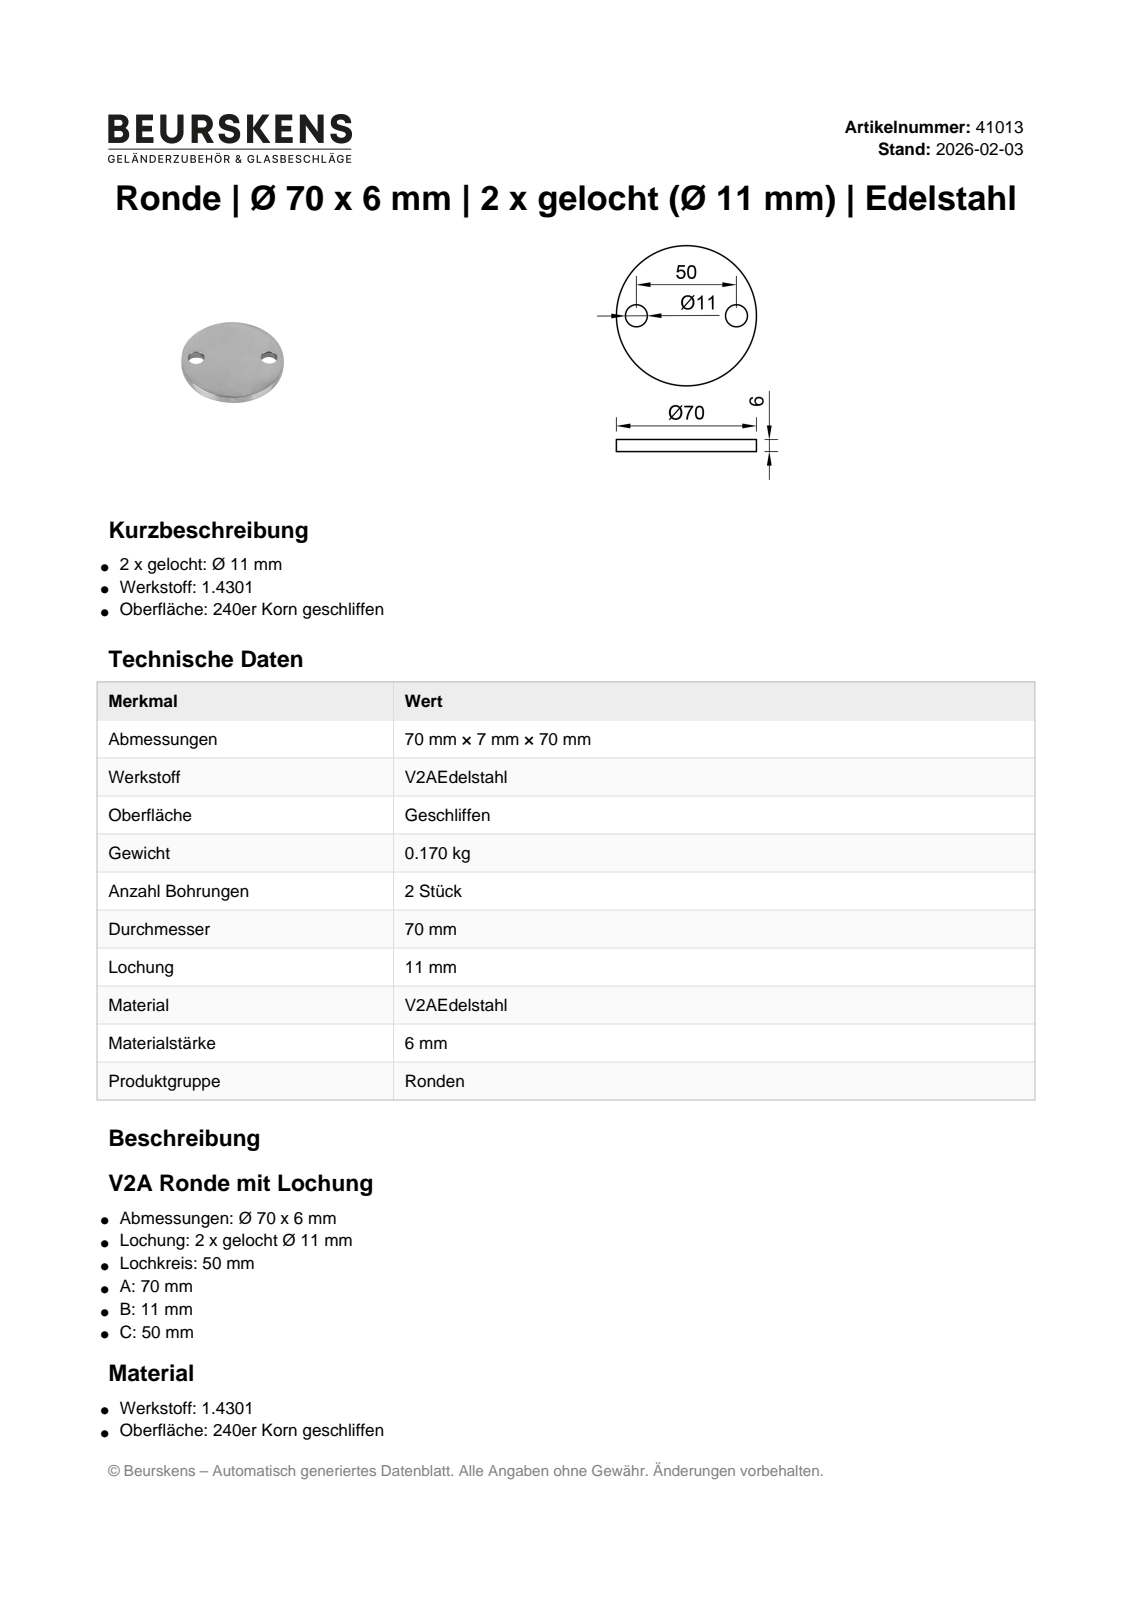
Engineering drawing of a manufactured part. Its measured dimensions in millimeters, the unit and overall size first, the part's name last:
Units: millimetres
Overall size (bounding box): 70 × 70 × 6
Round holes (diameter × count): ⌀11 ×2
Round bosses / shafts (diameter × count): ⌀70 ×1
Main face-to-face distances: 6
Hole centre spacings: 50
Volume: 21 950 mm³ · Surface area: 9 051 mm²
Bodies: 1 solid, 5 faces (2 planar, 3 cylindrical, 0 other)
Part name (STEP PRODUCT): 41013
STEP written by: Autodesk Inventor 2022 (AUTOMOTIVE_DESIGN)
